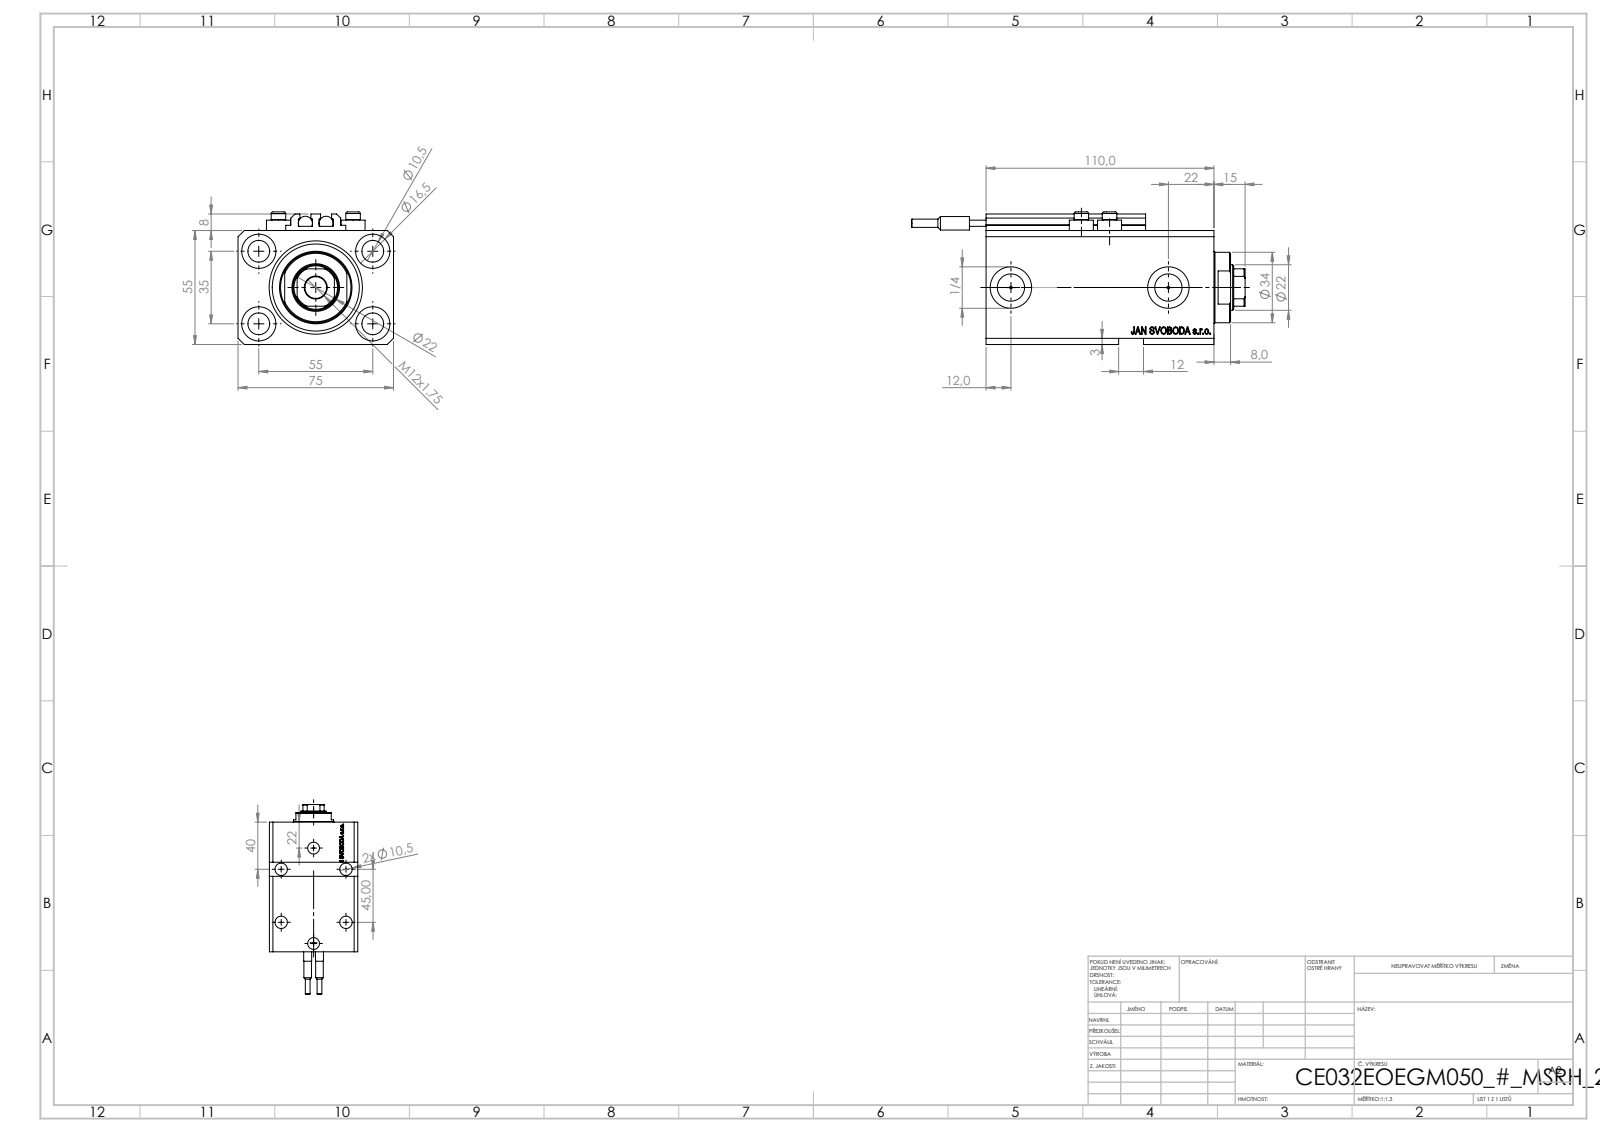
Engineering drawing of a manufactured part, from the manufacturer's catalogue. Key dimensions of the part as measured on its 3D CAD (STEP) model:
Part name (STEP PRODUCT): V250CE_VC_E; V250CE_E_Body; SWITCH_V250CE; V250CE_C_VCP (+1 more)
STEP written by: SolidWorks 2019 (CONFIG_CONTROL_DESIGN)
Units: millimetres
Bodies: 10 solids, 1136 faces (546 planar, 158 cylindrical, 432 other)
Overall size (bounding box): 161 × 75 × 64
Volume: 384 911 mm³ · Surface area: 98 392 mm²
Round holes (diameter × count): ⌀10.5 ×9, ⌀1.25 ×4, ⌀4 ×4, ⌀16.5 ×4, ⌀10 ×2, ⌀13.16 ×2, ⌀20 ×2, ⌀22 ×1, ⌀32 ×1, ⌀45 ×1
Round bosses / shafts (diameter × count): ⌀11.6 ×4, ⌀7 ×4, ⌀6.8 ×2, ⌀6.5 ×2, ⌀4 ×2, ⌀34 ×1
Partial cylindrical surfaces — rounded edges, fillets, slot ends (radius × count): R0.2 ×10, R10.5 ×1
Main face-to-face distances: 55, 75, 3, 15, 110, 57, 95, 9.9, 85.1, 100.1
Hole centre spacings: 32.6, 32.87, 55, 68.74, 13.6, 14.09, 23.05, 25.81
